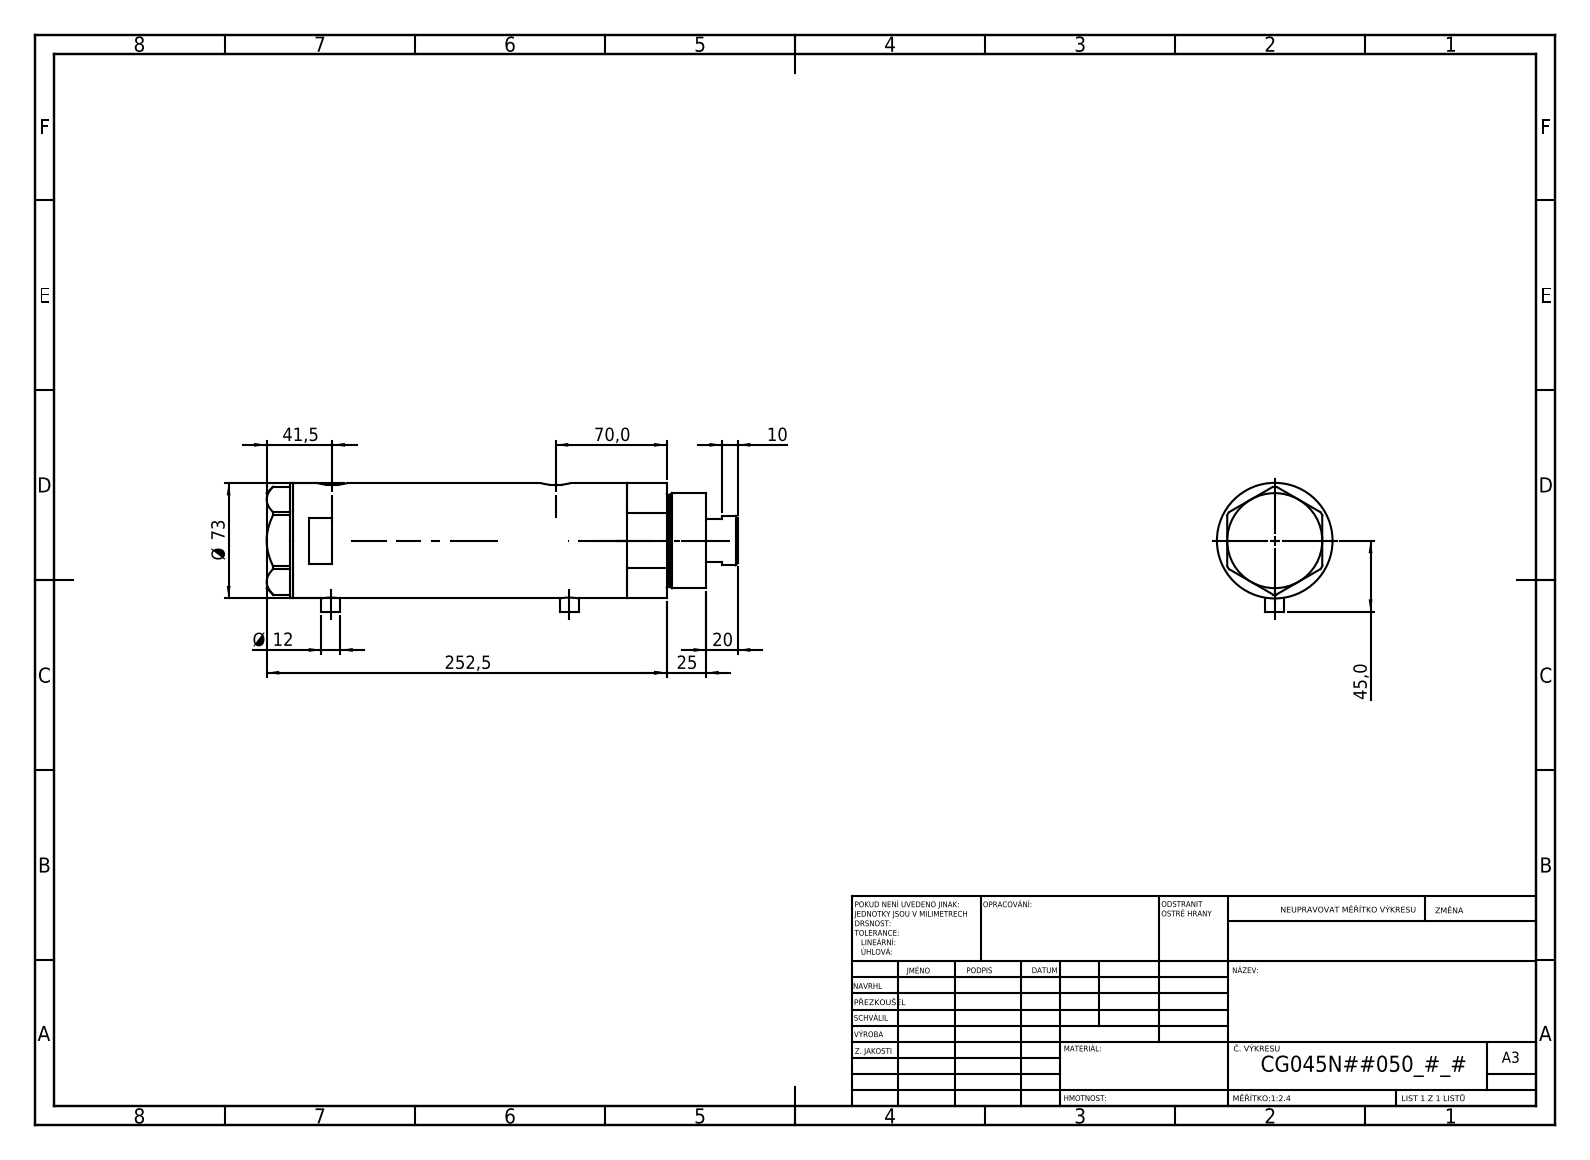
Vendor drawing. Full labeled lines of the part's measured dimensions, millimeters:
Part name (STEP PRODUCT): V270CG_BACK; V270CG_MIDDLE; V270CG_FRONT; V270CG_VC
STEP written by: SolidWorks 2019 (CONFIG_CONTROL_DESIGN)
Units: millimetres
Bodies: 4 solids, 120 faces (49 planar, 51 cylindrical, 20 other)
Overall size (bounding box): 297.5 × 81.5 × 73
Volume: 1 074 000 mm³ · Surface area: 171 994 mm²
Round holes (diameter × count): ⌀12.5 ×2, ⌀13.16 ×2, ⌀10.5 ×1, ⌀32 ×1, ⌀33.5 ×1, ⌀45 ×1, ⌀48 ×1, ⌀64 ×1
Round bosses / shafts (diameter × count): ⌀12 ×2, ⌀73 ×1, ⌀60 ×1, ⌀58 ×1, ⌀31 ×1
Partial cylindrical surfaces — rounded edges, fillets, slot ends (radius × count): R10 ×2
Main face-to-face distances: 166, 26, 140, 16.5, 42.5, 182.5, 2, 261, 277.5, 235
Hole centre spacings: 1, 8.5, 141, 142, 149.5, 150.5
